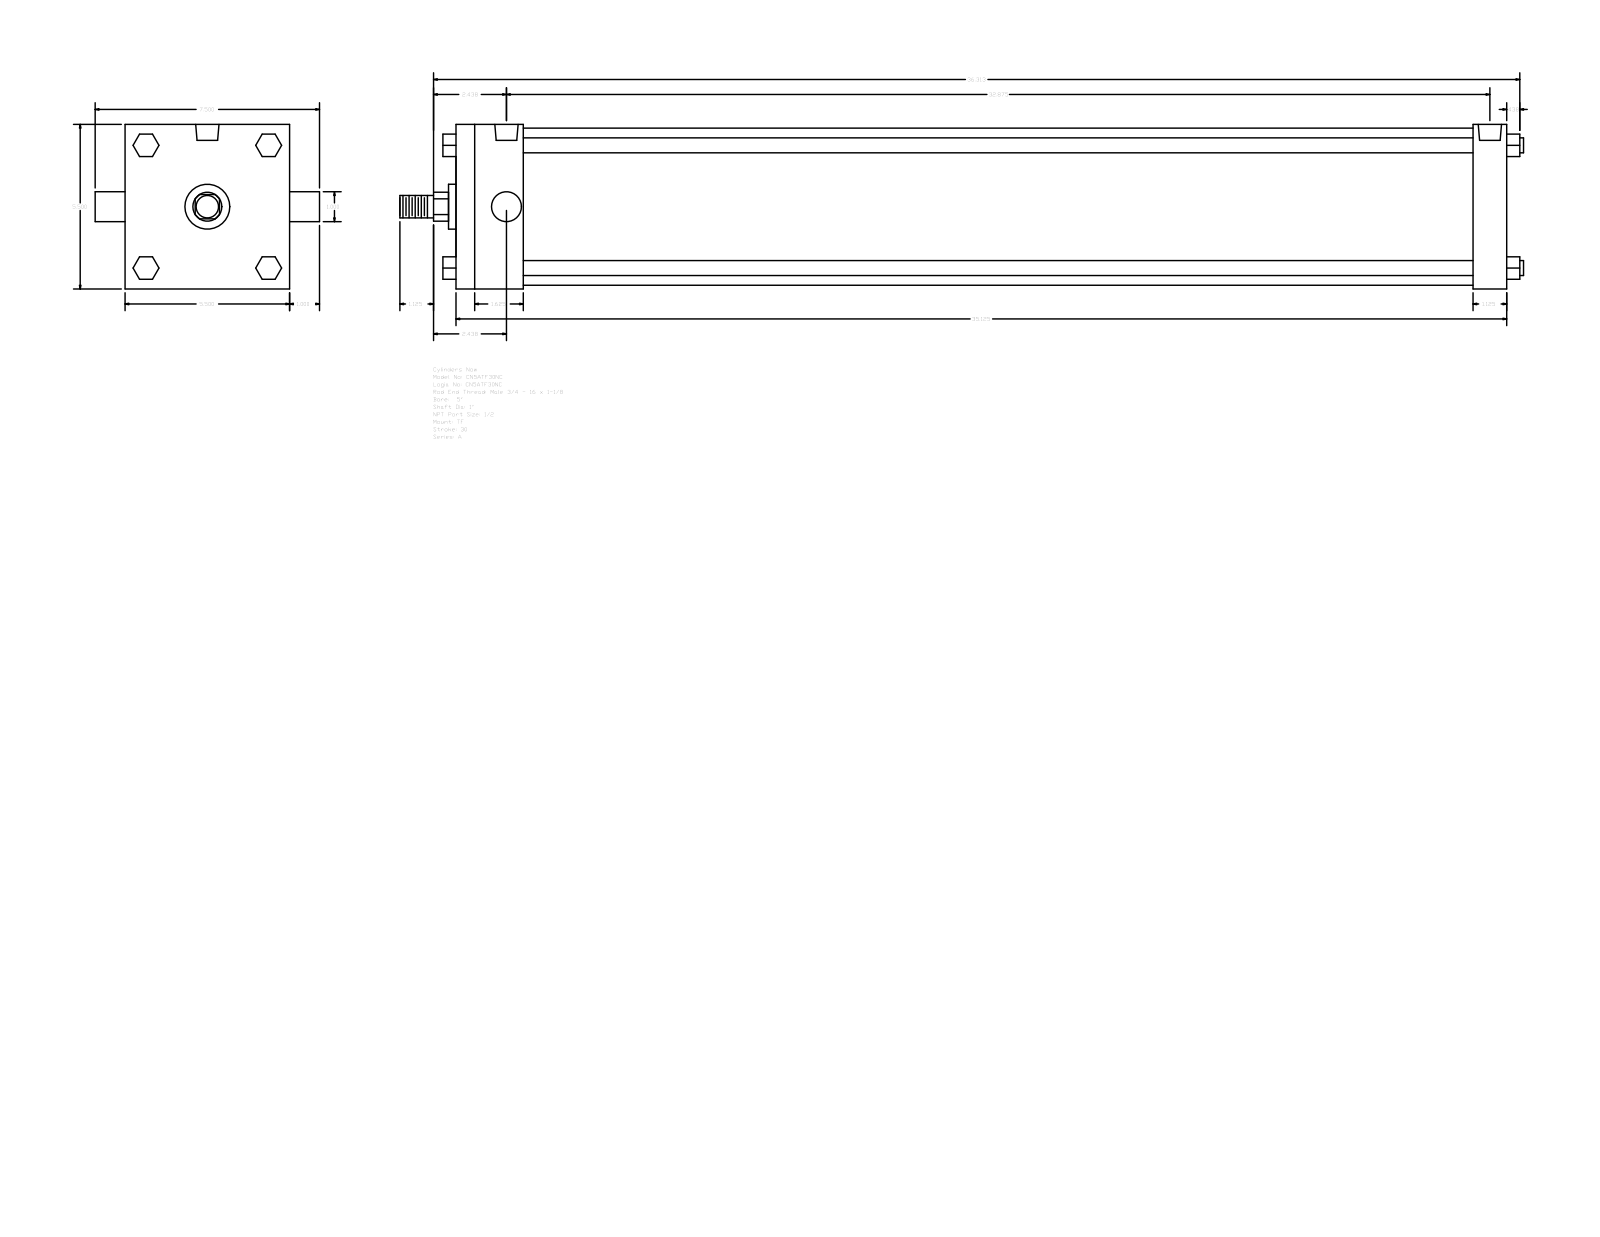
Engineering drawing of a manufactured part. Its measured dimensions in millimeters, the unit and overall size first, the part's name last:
Units: millimetres
Overall size (bounding box): 954.09 × 190.5 × 139.7
Round holes (diameter × count): ⌀8.73 ×3, ⌀19.77 ×2
Round bosses / shafts (diameter × count): ⌀12.7 ×4, ⌀25.4 ×2, ⌀133.35 ×1, ⌀38.1 ×1, ⌀19.05 ×1
Partial cylindrical surfaces — rounded edges, fillets, slot ends (radius × count): R12.29 ×1
Main face-to-face distances: 139.7, 892.18, 863.6, 28.58, 57.15, 806.45, 835.03, 19.05, 52.07, 90.18
Hole centre spacings: 2.39, 832.64, 830.25, 835.03
Bodies: 0 solids, 120 faces (92 planar, 28 cylindrical, 0 other)
Part name (STEP PRODUCT): A_TF__0500_1
STEP written by: GSSL Pune (CONFIG_CONTROL_DESIGN)
